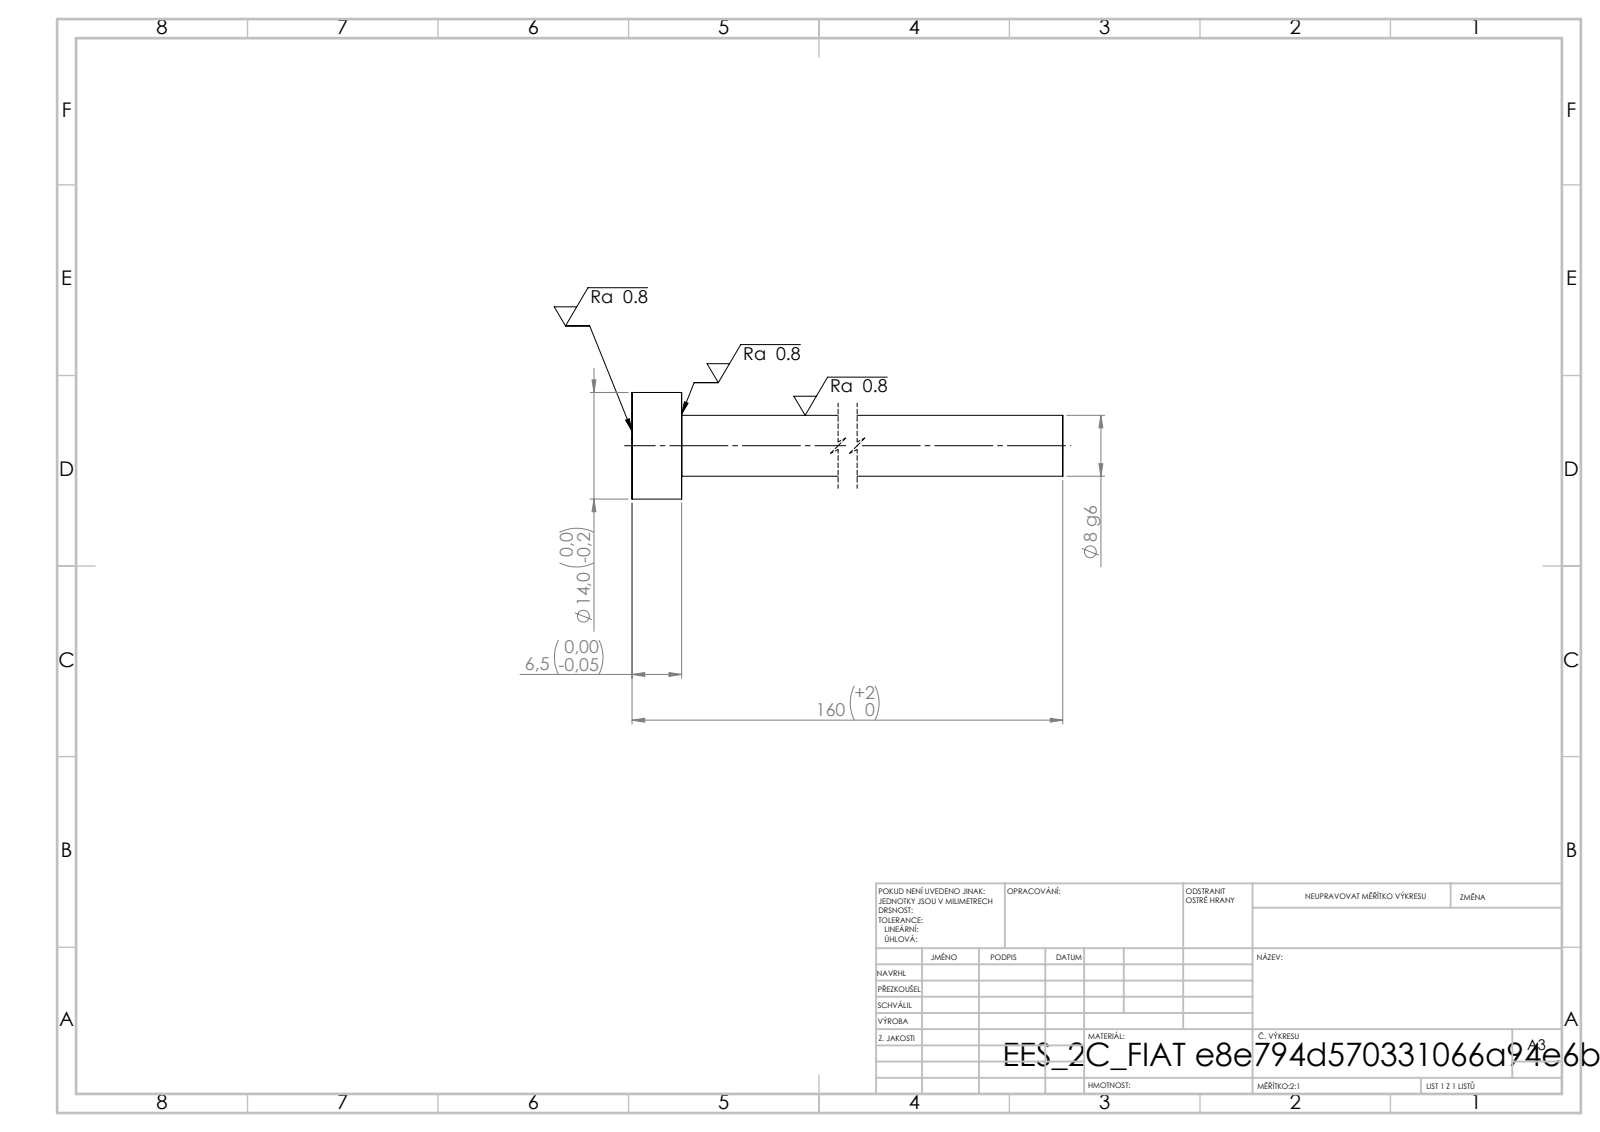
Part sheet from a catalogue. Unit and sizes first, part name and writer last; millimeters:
Units: millimetres
Overall size (bounding box): 160 × 14 × 14
Round bosses / shafts (diameter × count): ⌀14 ×1, ⌀8 ×1
Main face-to-face distances: 6.5, 160, 153.5
Volume: 8 716 mm³ · Surface area: 4 452 mm²
Bodies: 1 solid, 7 faces (3 planar, 4 cylindrical, 0 other)
STEP written by: SolidWorks 2019 (CONFIG_CONTROL_DESIGN)
